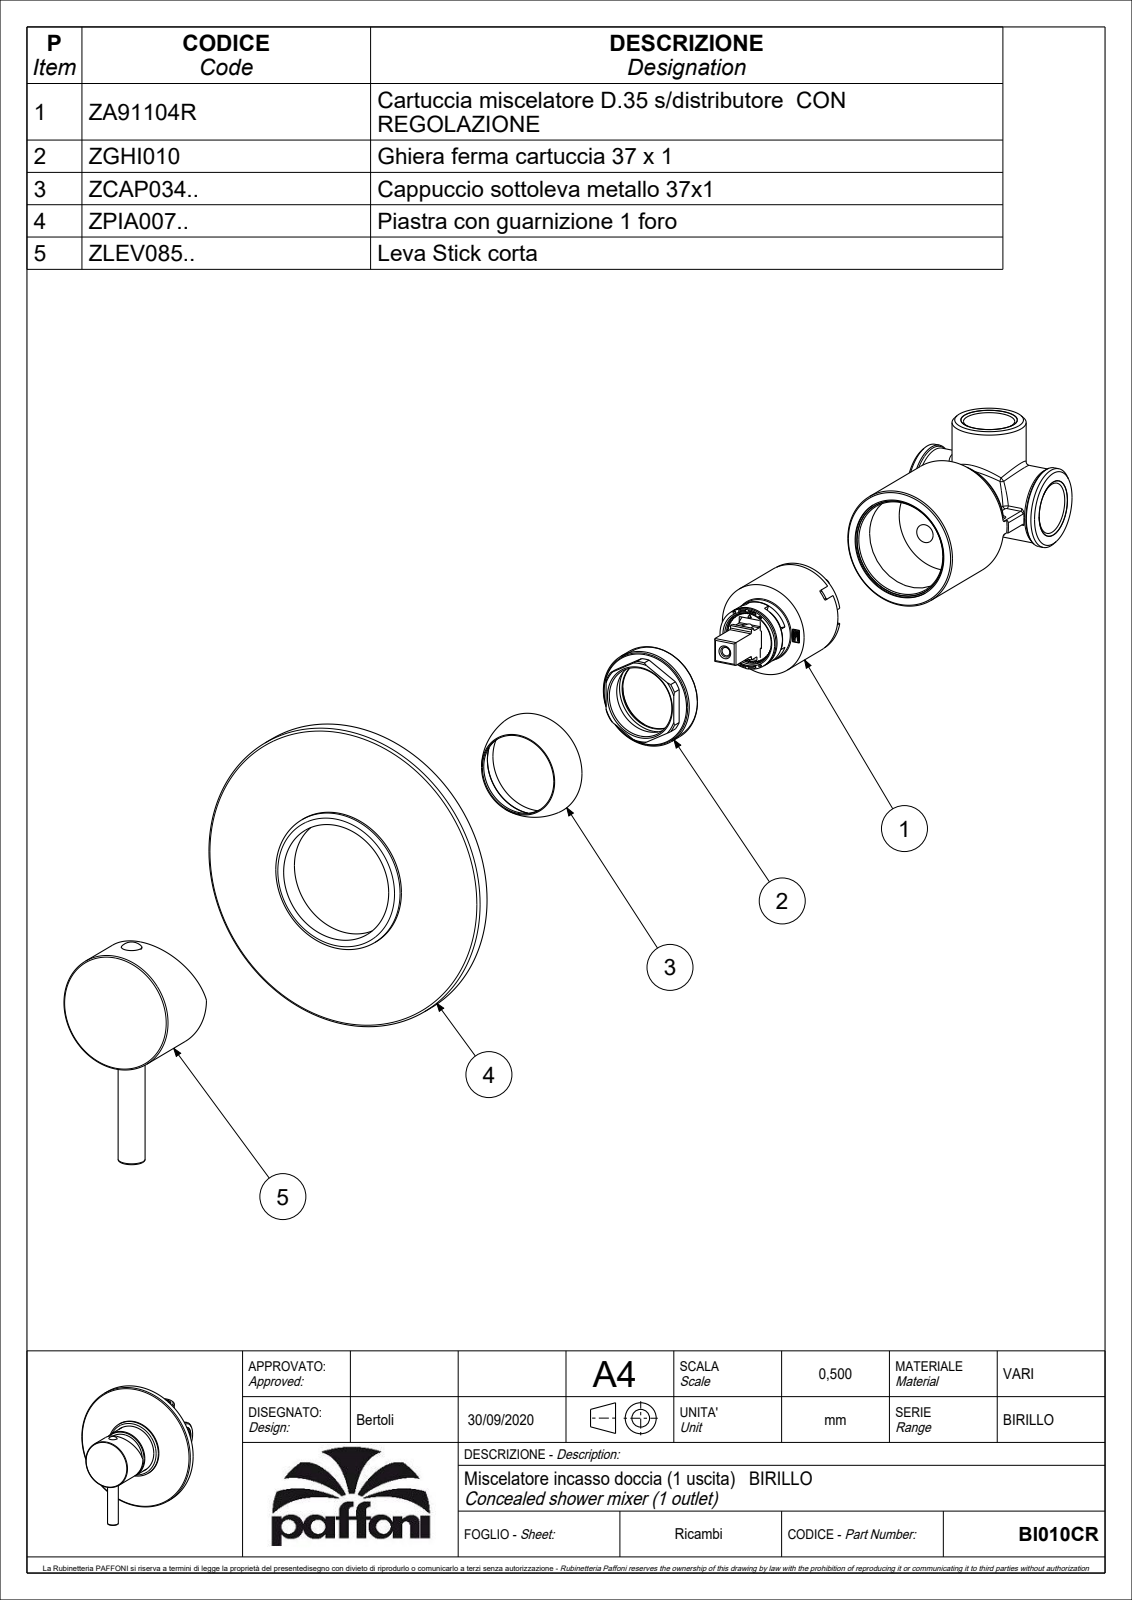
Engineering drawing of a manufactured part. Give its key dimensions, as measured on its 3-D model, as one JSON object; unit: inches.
{"part_name": "BI010CR", "step_written_by": "CREO PARAMETRIC BY PTC INC, 2020044 (CONFIG_CONTROL_DESIGN)", "units": "inches", "bodies": {"solids": 2, "faces": 989, "planar": 577, "cylindrical": 222, "other": 190}, "overall_size": [4.724, 4.567, 2.389], "volume_in3": 3.671, "surface_area_in2": 95.99, "round_holes": [[0.157, 2], [0.118, 1], [0.13, 1], [0.197, 1], [0.217, 1], [0.768, 1], [0.783, 1], [1.055, 1], [1.142, 1], [1.22, 1], [1.276, 1], [1.417, 1]], "round_bosses_or_shafts": [[4.567, 1], [2.087, 1], [1.764, 1], [1.752, 1], [1.378, 1], [1.268, 1], [0.925, 1], [0.921, 1]], "partial_cylinders_radius": [[0.02, 35], [0.006, 11], [0.012, 4], [0.039, 2], [0.276, 1], [0.366, 1], [0.427, 1], [0.443, 1]], "face_to_face_distances": [0.453, 0.091, 0.157, 2.217, 2.126, 0.815, 0.059, 0.098, 0.217, 0.354], "hole_center_spacings": [0.461]}
